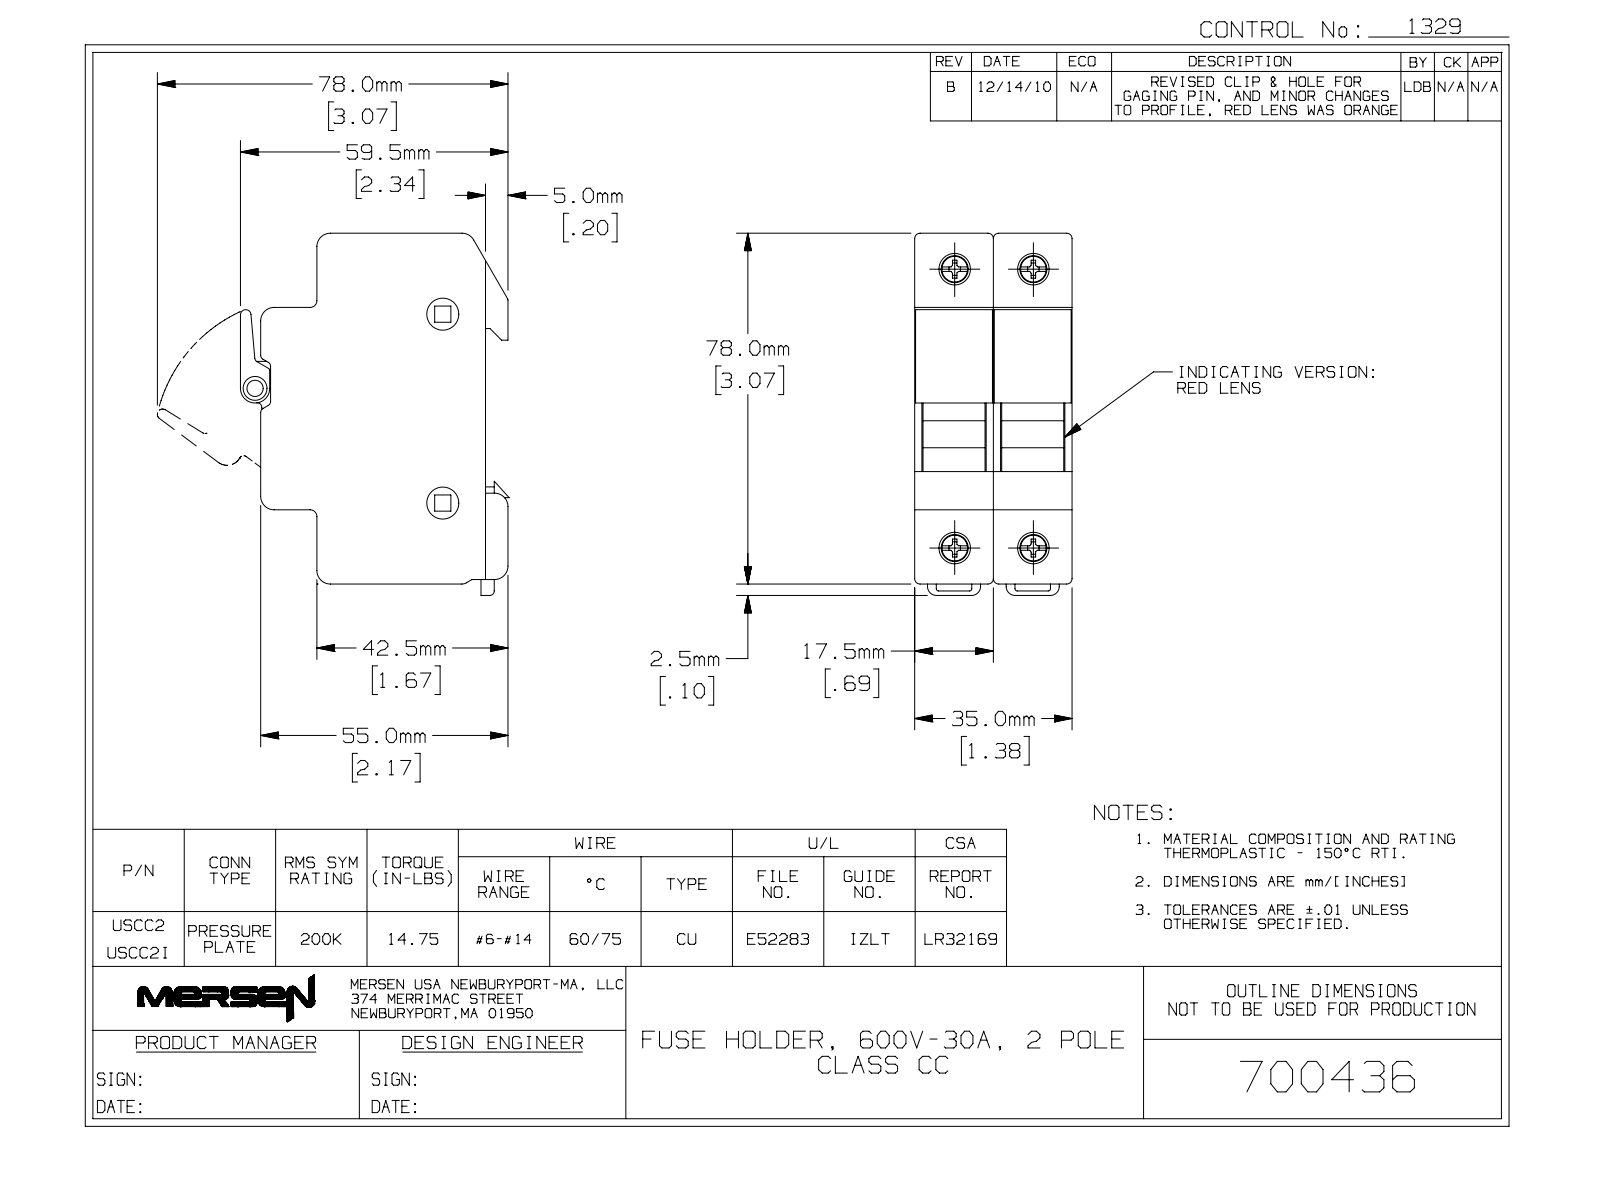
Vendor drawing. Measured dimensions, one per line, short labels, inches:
name: (__)^USCC2I_700436; 700436; MR8.140.626 USM ____^USCC2I_700436; ^USCC2I_700436 (+8 more)
written by: SolidWorks 2021 (AUTOMOTIVE_DESIGN)
unit: in
bodies: 48 solids, 5768 faces (3528 planar, 1060 cylindrical, 1180 other)
size: 3.15 × 2.362 × 1.386
volume: 3.376 in³; area: 133.5 in²
holes: 6× ⌀0.283, 4× ⌀0.165, 4× ⌀0.256, 1× ⌀0.079, 1× ⌀0.118, 1× ⌀0.127, 1× ⌀0.205, 1× ⌀0.213
bosses: 14× ⌀0.059, 5× ⌀0.197, 4× ⌀0.331, 4× ⌀0.256, 4× ⌀0.142, 2× ⌀0.098, 1× ⌀0.354
rounds: 124× R0.02, 67× R0.039, 58× R0.012, 32× R0.024, 29× R0.079, 24× R0.063, 16× R0.059, 8× R0.008
face distances: 0.693, 0.063, 0.63, 0.567, 0.756, 1.323, 1.386, 0.024, 1.26, 0.079
hole spacings: 0.693, 2.434, 0.691, 0.693, 0.693, 0.695, 2.42, 2.423
